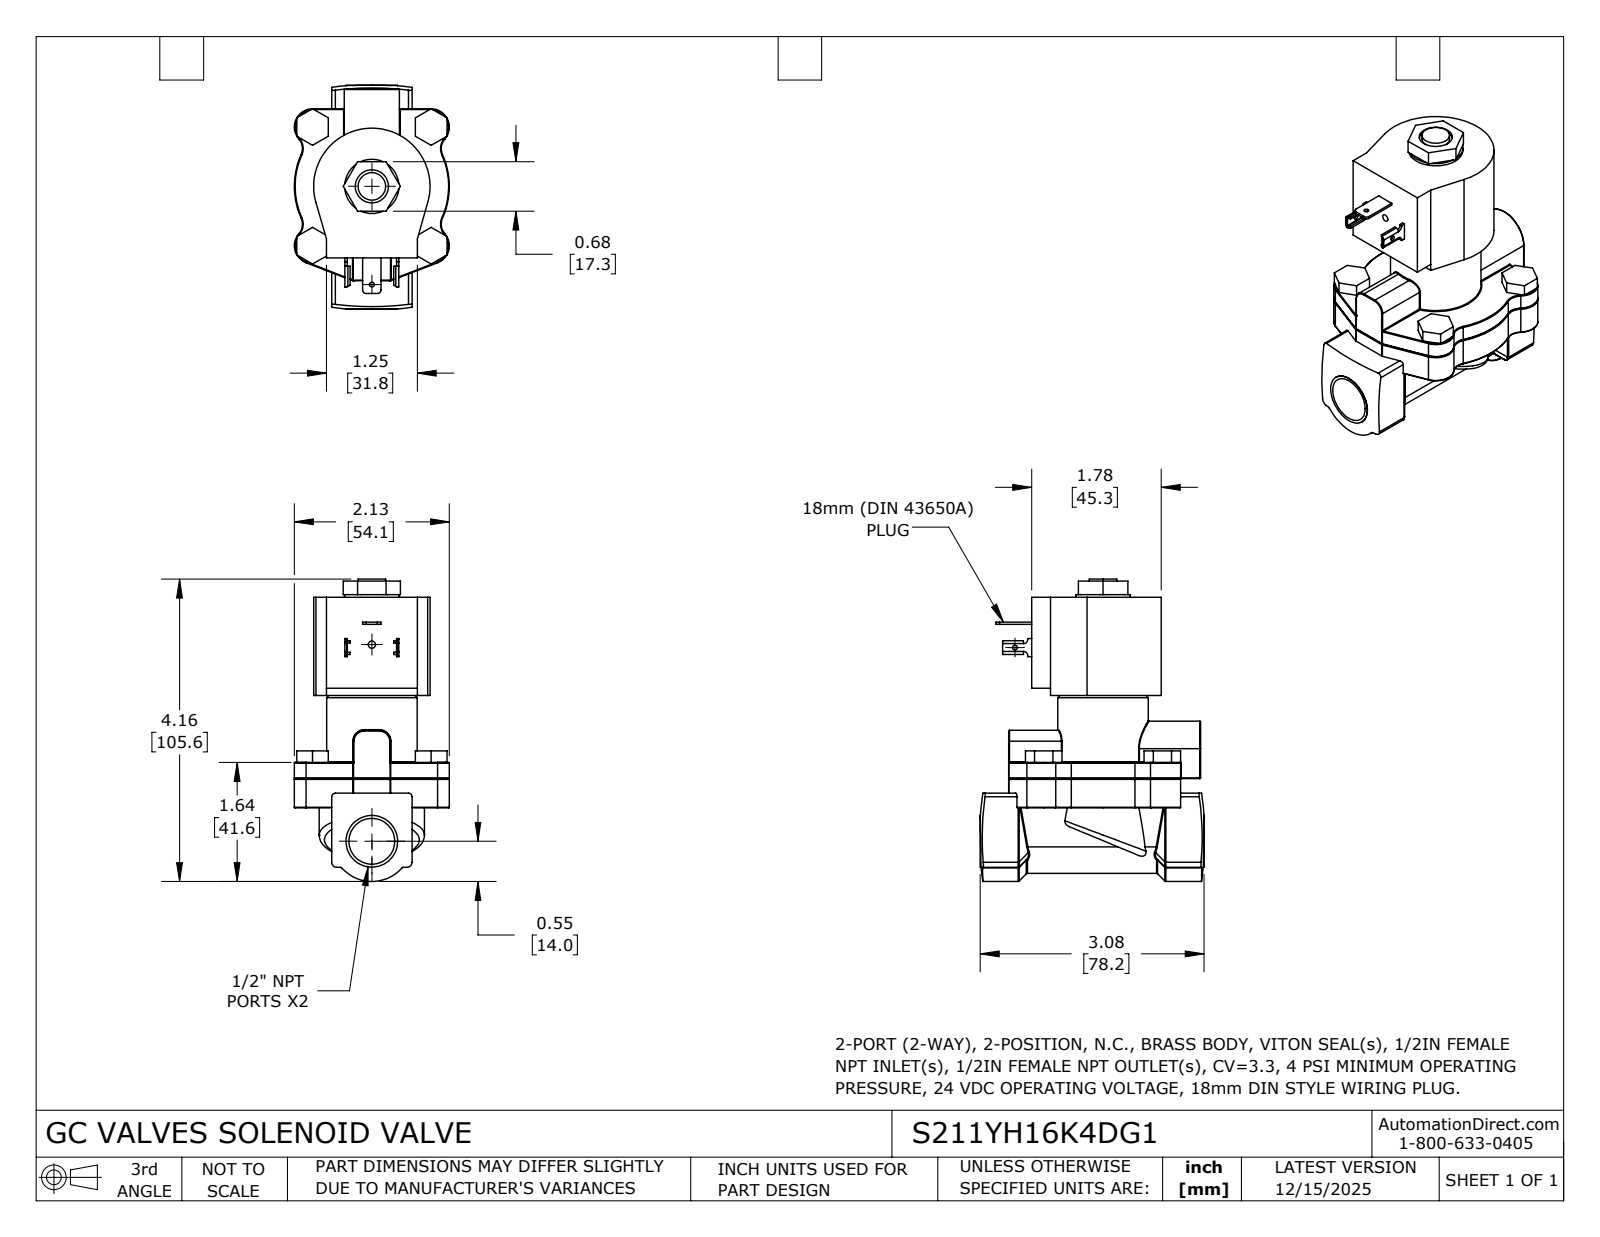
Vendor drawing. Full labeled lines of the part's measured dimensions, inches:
Part name (STEP PRODUCT): S211YH16K4DG1
STEP written by: SolidWorks 2024 (CONFIG_CONTROL_DESIGN)
Units: inches
Bodies: 1 solid, 447 faces (159 planar, 149 cylindrical, 139 other)
Overall size (bounding box): 4.156 × 3.077 × 2.131
Volume: 10.29 in³ · Surface area: 43.83 in²
Round holes (diameter × count): ⌀0.066 ×1, ⌀0.067 ×1, ⌀0.1 ×1, ⌀0.456 ×1, ⌀0.63 ×1
Round bosses / shafts (diameter × count): ⌀1.245 ×1, ⌀0.746 ×1, ⌀0.71 ×1, ⌀0.377 ×1
Partial cylindrical surfaces — rounded edges, fillets, slot ends (radius × count): R0.01 ×32, R0.02 ×14, R0.006 ×4, R0.041 ×4, R0.05 ×4, R0.1 ×4, R0.2 ×4, R0.25 ×4
Main face-to-face distances: 2.27, 0.625, 2.895, 1.545, 0.92, 1.35, 1.105, 0.785, 0.16, 0.76
Hole centre spacings: 1.35, 2.703
